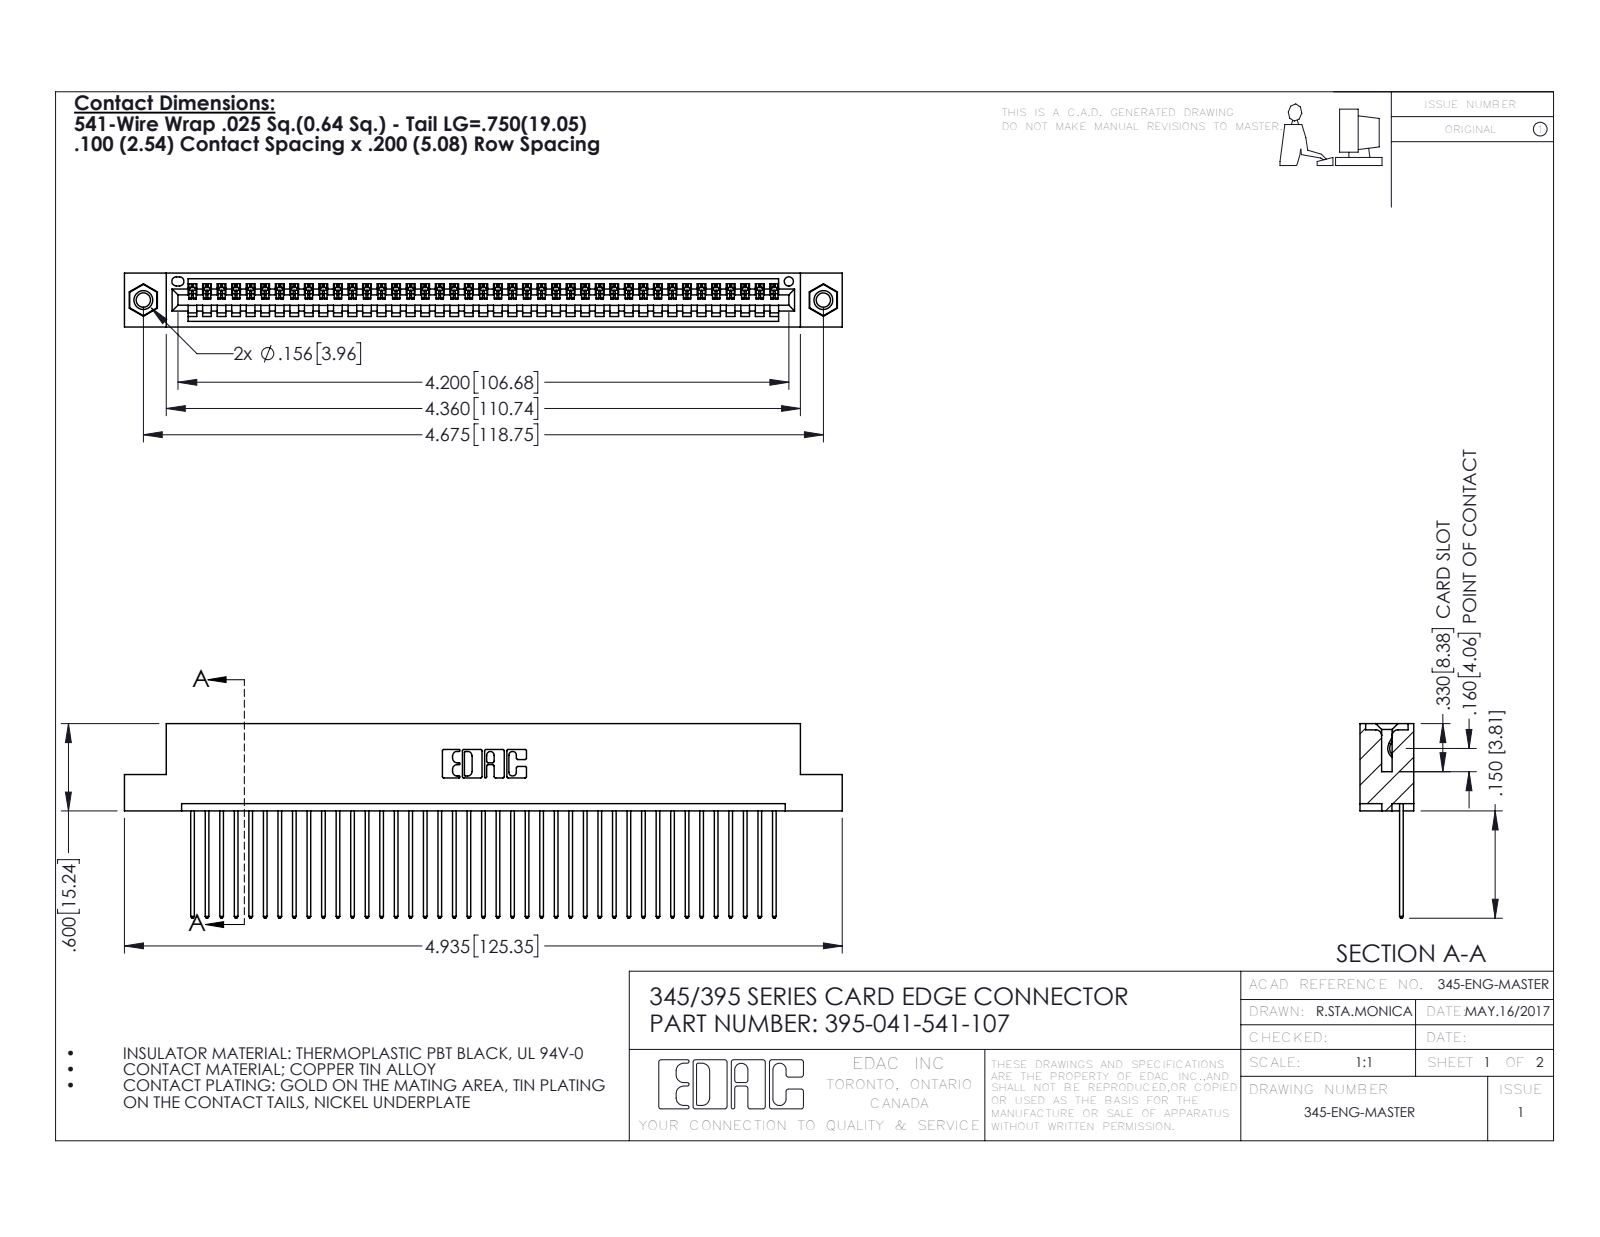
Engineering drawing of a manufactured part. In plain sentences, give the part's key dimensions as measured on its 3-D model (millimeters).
The part is named "395-041-541-107; 345-250-001_345-250-005-103; 345-292-001_345-293-141; 345 Part_Flush Mounting Lugs - 0.156 Dia-TI". Its 3-D file was written by "SolidWorks 2016 (CONFIG_CONTROL_DESIGN)". It is 44 solids with 2564 faces: 1752 planar, 796 cylindrical and 16 other. Overall it measures 125.3 by 34 by 9.4 millimeters. Its volume is 12 000 cubic millimeters and its surface area 16 790 square millimeters. Round holes: 2 of diameter 2.5, 2 of diameter 3.2, 2 of diameter 4, 1 of diameter 1.6. Round bosses or shafts: 2 of diameter 3.9. Partial cylindrical surfaces (rounded edges, fillets, slot ends): 82 of radius 0.2, 82 of radius 0.3, 22 of radius 0.3, 6 of radius 0.2, 6 of radius 0.8, 3 of radius 0.7, 2 of radius 0.8, 2 of radius 1. The main face-to-face distances are 1.8, 7.6, 2.5, 6.9, 0.6, 9.4, 5.1, 5.7, 3.8, 1.8. The hole center spacings are 6.9, 112.8, 118.7.
